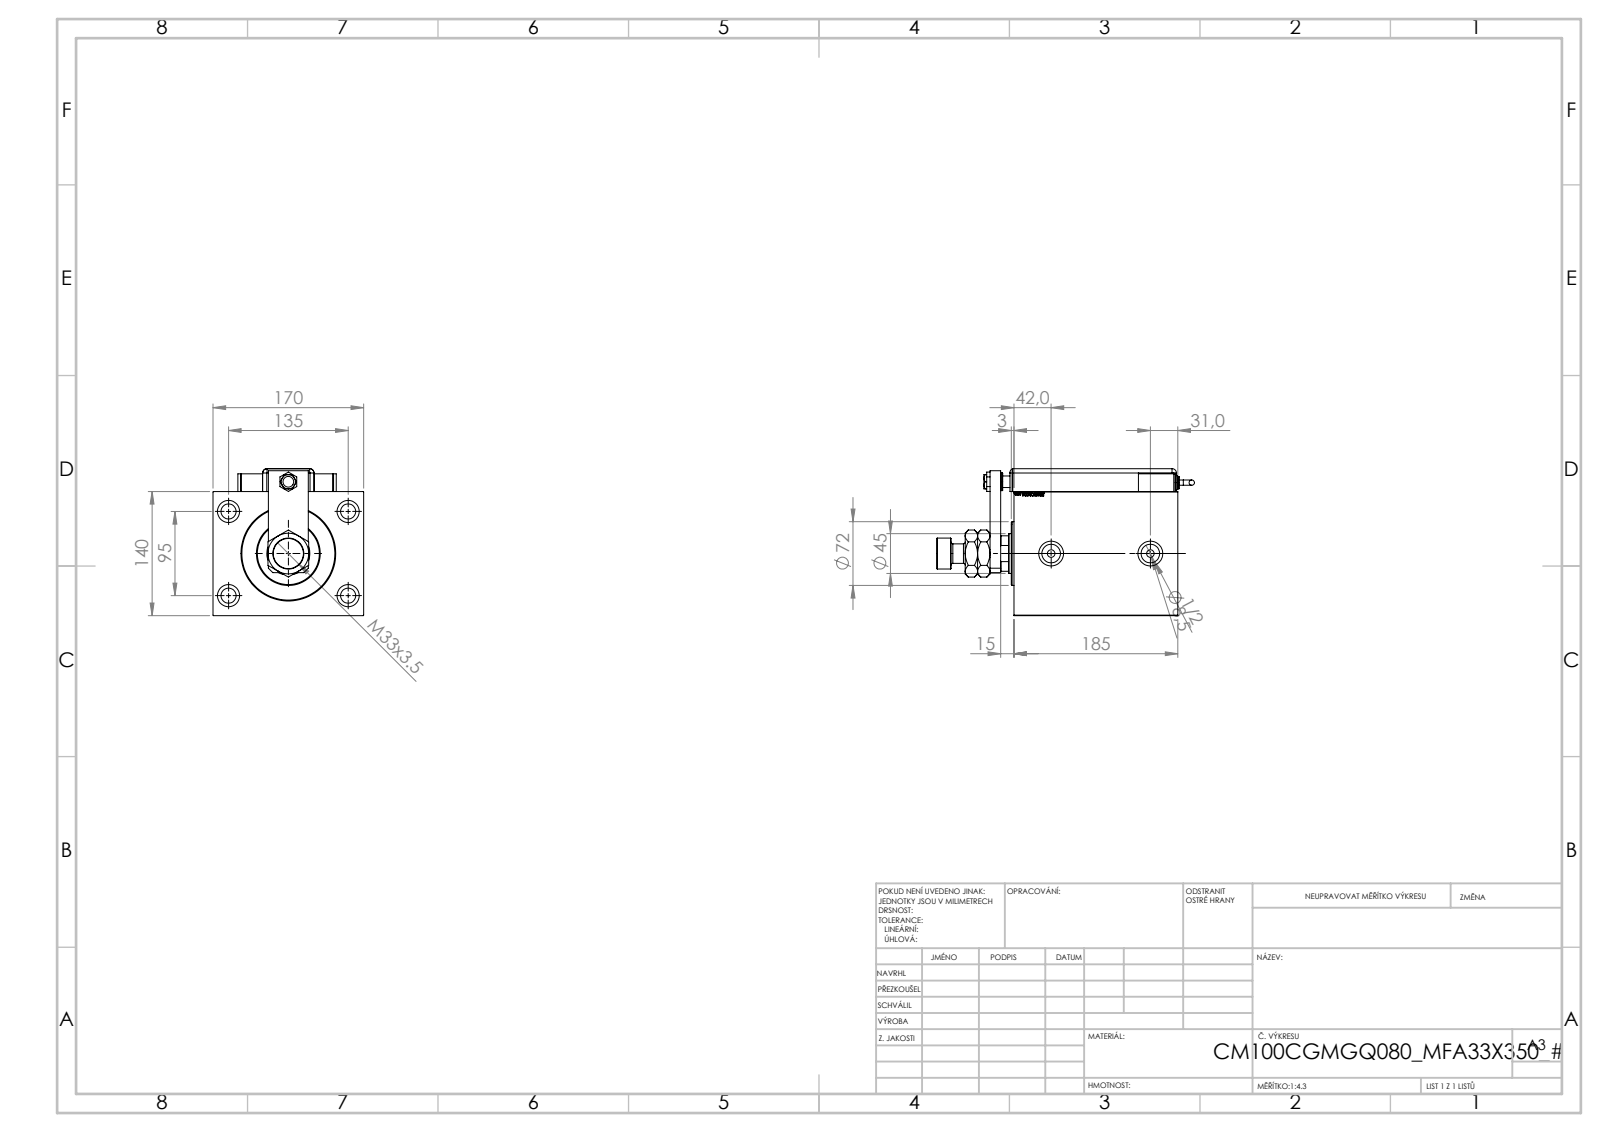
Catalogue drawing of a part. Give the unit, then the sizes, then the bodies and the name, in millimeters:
Units: millimetres
Overall size (bounding box): 290.76 × 170 × 165.8
Round holes (diameter × count): ⌀17 ×4, ⌀25 ×4, ⌀4 ×2, ⌀8 ×2, ⌀8.5 ×2, ⌀20.96 ×2, ⌀28 ×2, ⌀12 ×1, ⌀13 ×1, ⌀14 ×1, ⌀31.5 ×1, ⌀33 ×1
Round bosses / shafts (diameter × count): ⌀20 ×3, ⌀16 ×2, ⌀14 ×2, ⌀6 ×2, ⌀72 ×1, ⌀35 ×1, ⌀22 ×1
Partial cylindrical surfaces — rounded edges, fillets, slot ends (radius × count): R5 ×9, R10 ×1, R22 ×1
Main face-to-face distances: 170, 140, 3, 185, 26, 159, 15, 25.8, 165.8, 80
Hole centre spacings: 82.54, 75.36, 95, 135, 145.15, 165.08, 20, 81
Volume: 3 972 000 mm³ · Surface area: 428 334 mm²
Bodies: 14 solids, 1301 faces (631 planar, 121 cylindrical, 549 other)
Part name (STEP PRODUCT): ZARAZKA_Q; SWITCH Q; V450CM_C_VCP; MAGNETIC SWITCH Q (+7 more)
STEP written by: SolidWorks 2019 (CONFIG_CONTROL_DESIGN)
